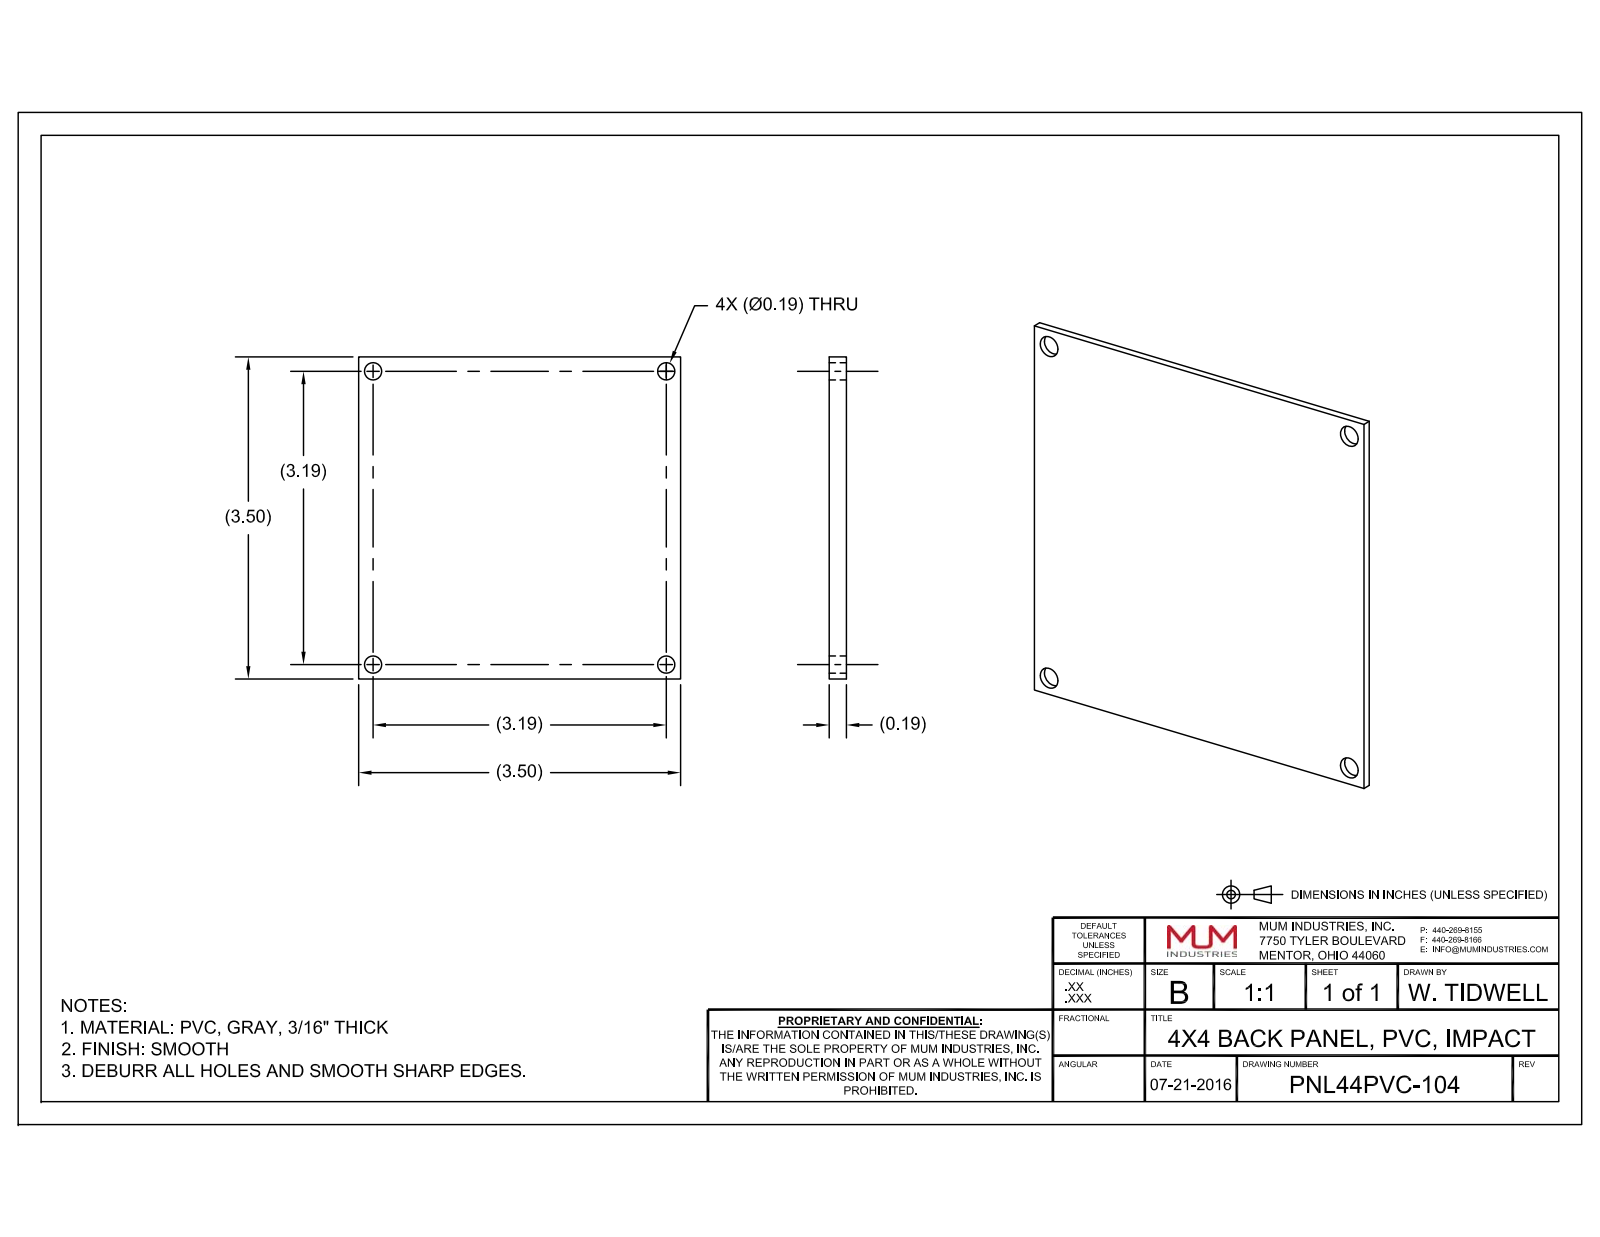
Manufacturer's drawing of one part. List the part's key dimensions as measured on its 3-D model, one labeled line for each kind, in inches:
Part name (STEP PRODUCT): PNL44PVC-104; 9912597-82-10; PVCBP44-IMP_ASM
STEP written by: CREO PARAMETRIC BY PTC INC, 2016050 (CONFIG_CONTROL_DESIGN)
Units: inches
Bodies: 5 solids, 422 faces (110 planar, 152 cylindrical, 160 other)
Overall size (bounding box): 3.509 × 3.509 × 0.49
Volume: 2.327 in³ · Surface area: 29.39 in²
Round holes (diameter × count): ⌀0.187 ×4
Round bosses / shafts (diameter × count): ⌀0.322 ×4, ⌀0.164 ×4, ⌀0.119 ×4
Main face-to-face distances: 0.187, 3.5, 0.302, 0.115, 0.237, 0.049, 0.066, 3.14, 0.375, 0.424
Hole centre spacings: 3.187, 4.507
